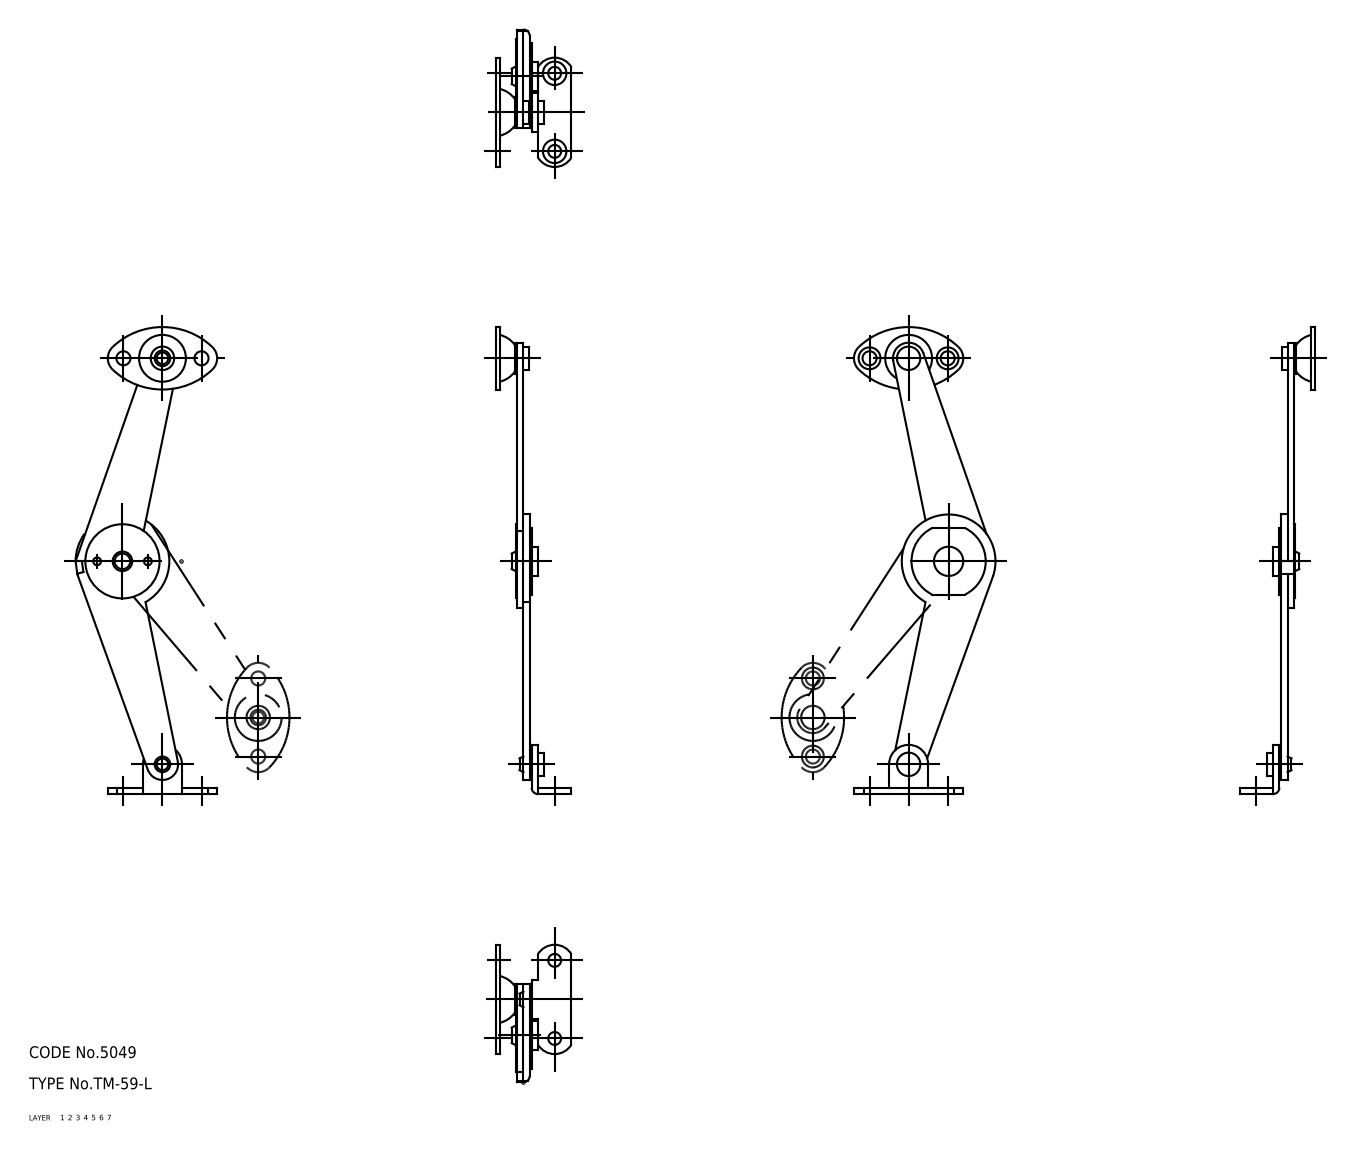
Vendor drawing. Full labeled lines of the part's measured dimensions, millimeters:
Part name (STEP PRODUCT): rivet_B2; rivet_B1; washer; ball (+7 more)
STEP written by: CADfix (AUTOMOTIVE_DESIGN)
Units: millimetres
Bodies: 12 solids, 135 faces (0 planar, 0 cylindrical, 135 other)
Overall size (bounding box): 119.6 × 36.25 × 19.4
Volume: 4 272 mm³ · Surface area: 7 131 mm²
